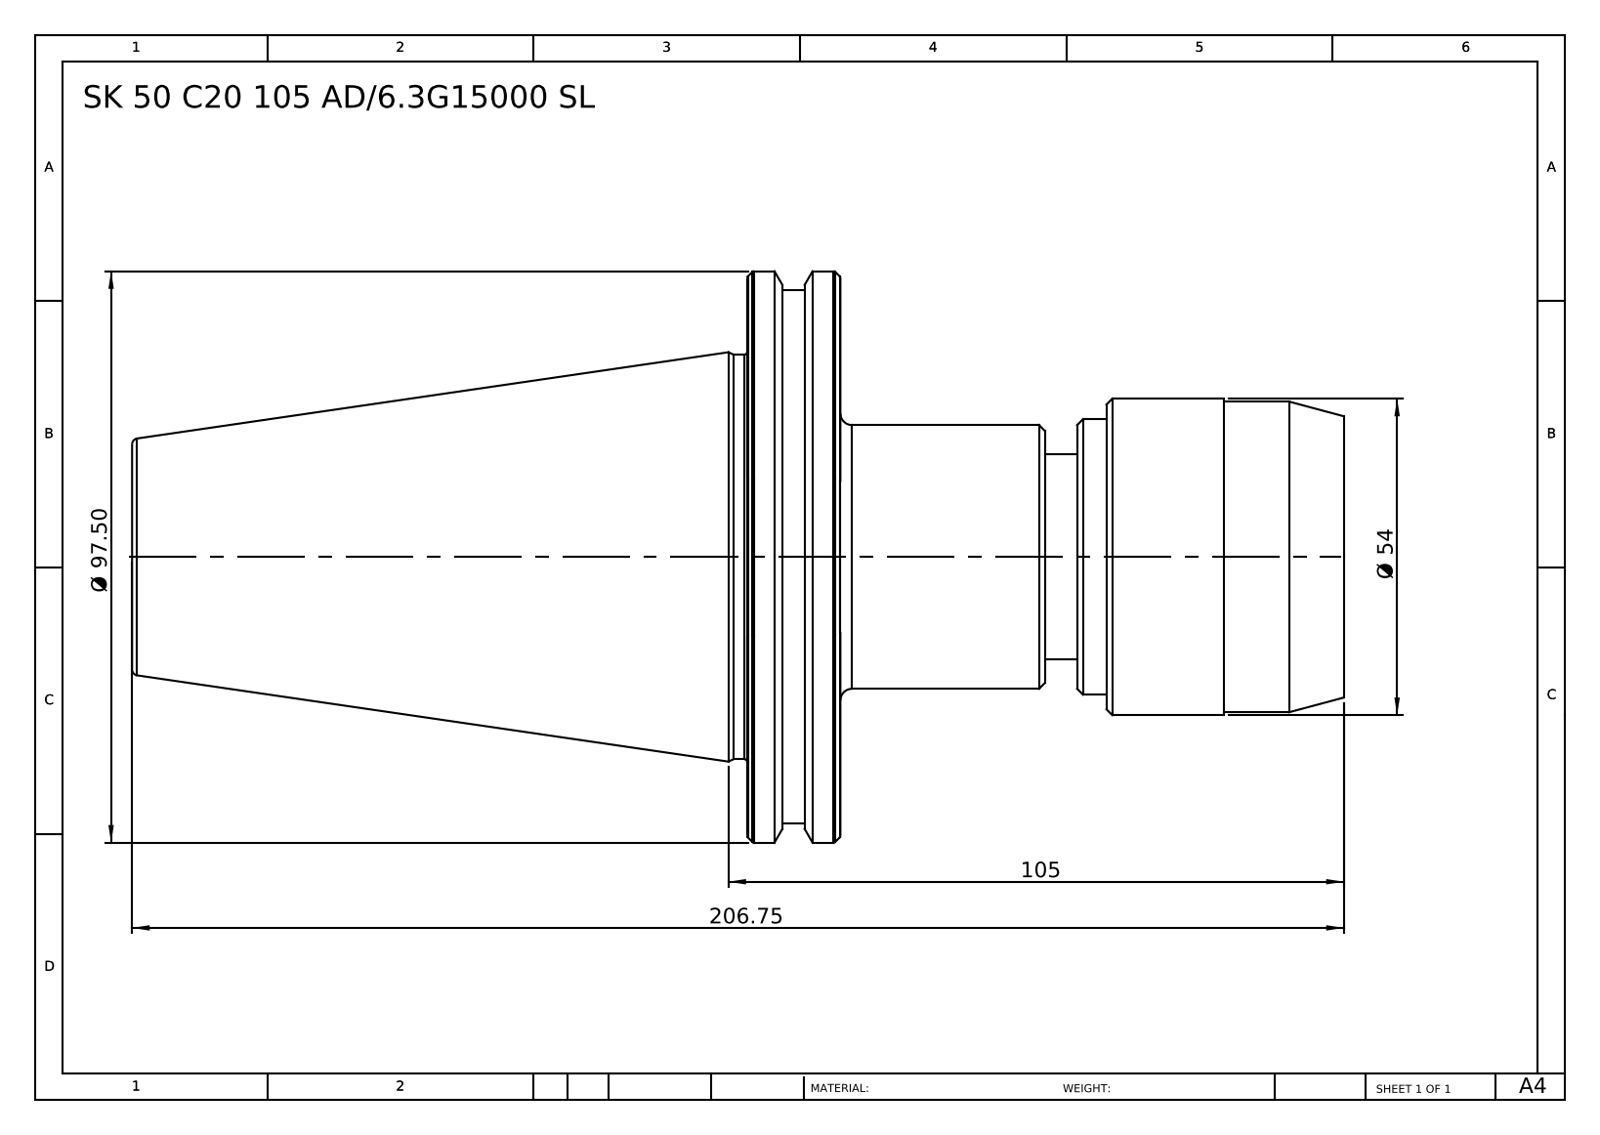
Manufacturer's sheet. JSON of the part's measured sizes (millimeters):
{"part_name": "SK 50 C20 105 AD-6.3G15000 SL", "step_written_by": "SolidWorks 2014 (CONFIG_CONTROL_DESIGN)", "units": "millimeters", "bodies": {"solids": 1, "faces": 82, "planar": 10, "cylindrical": 18, "other": 54}, "overall_size": [206.75, 97.5, 97.5], "volume_mm3": 532037, "surface_area_mm2": 51516, "round_bosses_or_shafts": [[97.5, 1], [91, 1], [69, 1], [54, 1], [53, 1], [47, 1], [45, 1], [35, 1]], "face_to_face_distances": [15.9, 85.9, 101.8, 206.75, 120.85, 104.95, 45.5, 40.4, 56.3, 161.25]}
